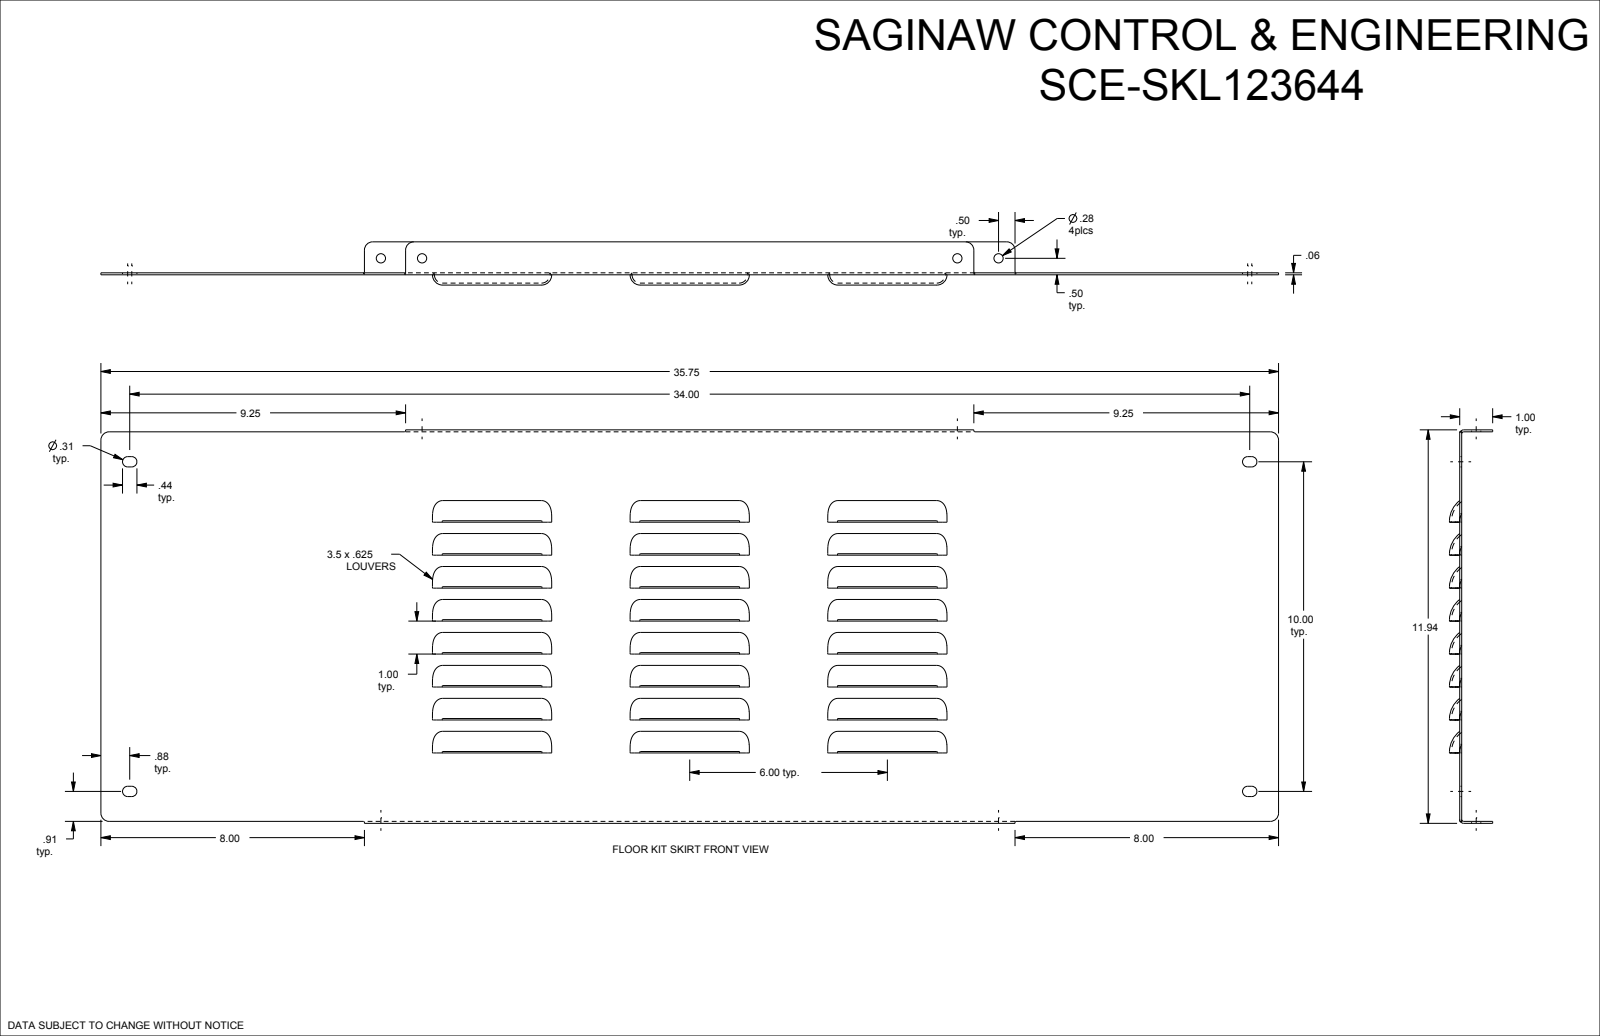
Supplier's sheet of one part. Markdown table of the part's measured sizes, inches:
| quantity | value |
| --- | --- |
| part name | SCE-SKL123644 |
| STEP written by | SolidWorks 2019 (CONFIG_CONTROL_DESIGN) |
| units | inches |
| bodies | 1 solid, 446 faces (122 planar, 72 cylindrical, 252 other) |
| overall size | 35.75 × 11.938 × 1.312 |
| volume | 28.14 in³ |
| surface area | 956.6 in² |
| round holes (diameter × count) | 0.281 × 4 |
| partial cylindrical surfaces (radius × count) | 0.156 × 8, 0.25 × 8, 0.74 × 8, 0.8 × 8, 0.06 × 2, 0.12 × 2 |
| main face-to-face distances | 0.06, 0.06, 11.878, 11.817, 11.938, 1, 2, 0.312, 3, 4 |
| hole center spacings | 1.25, 17.5, 16.25, 18.75 |
